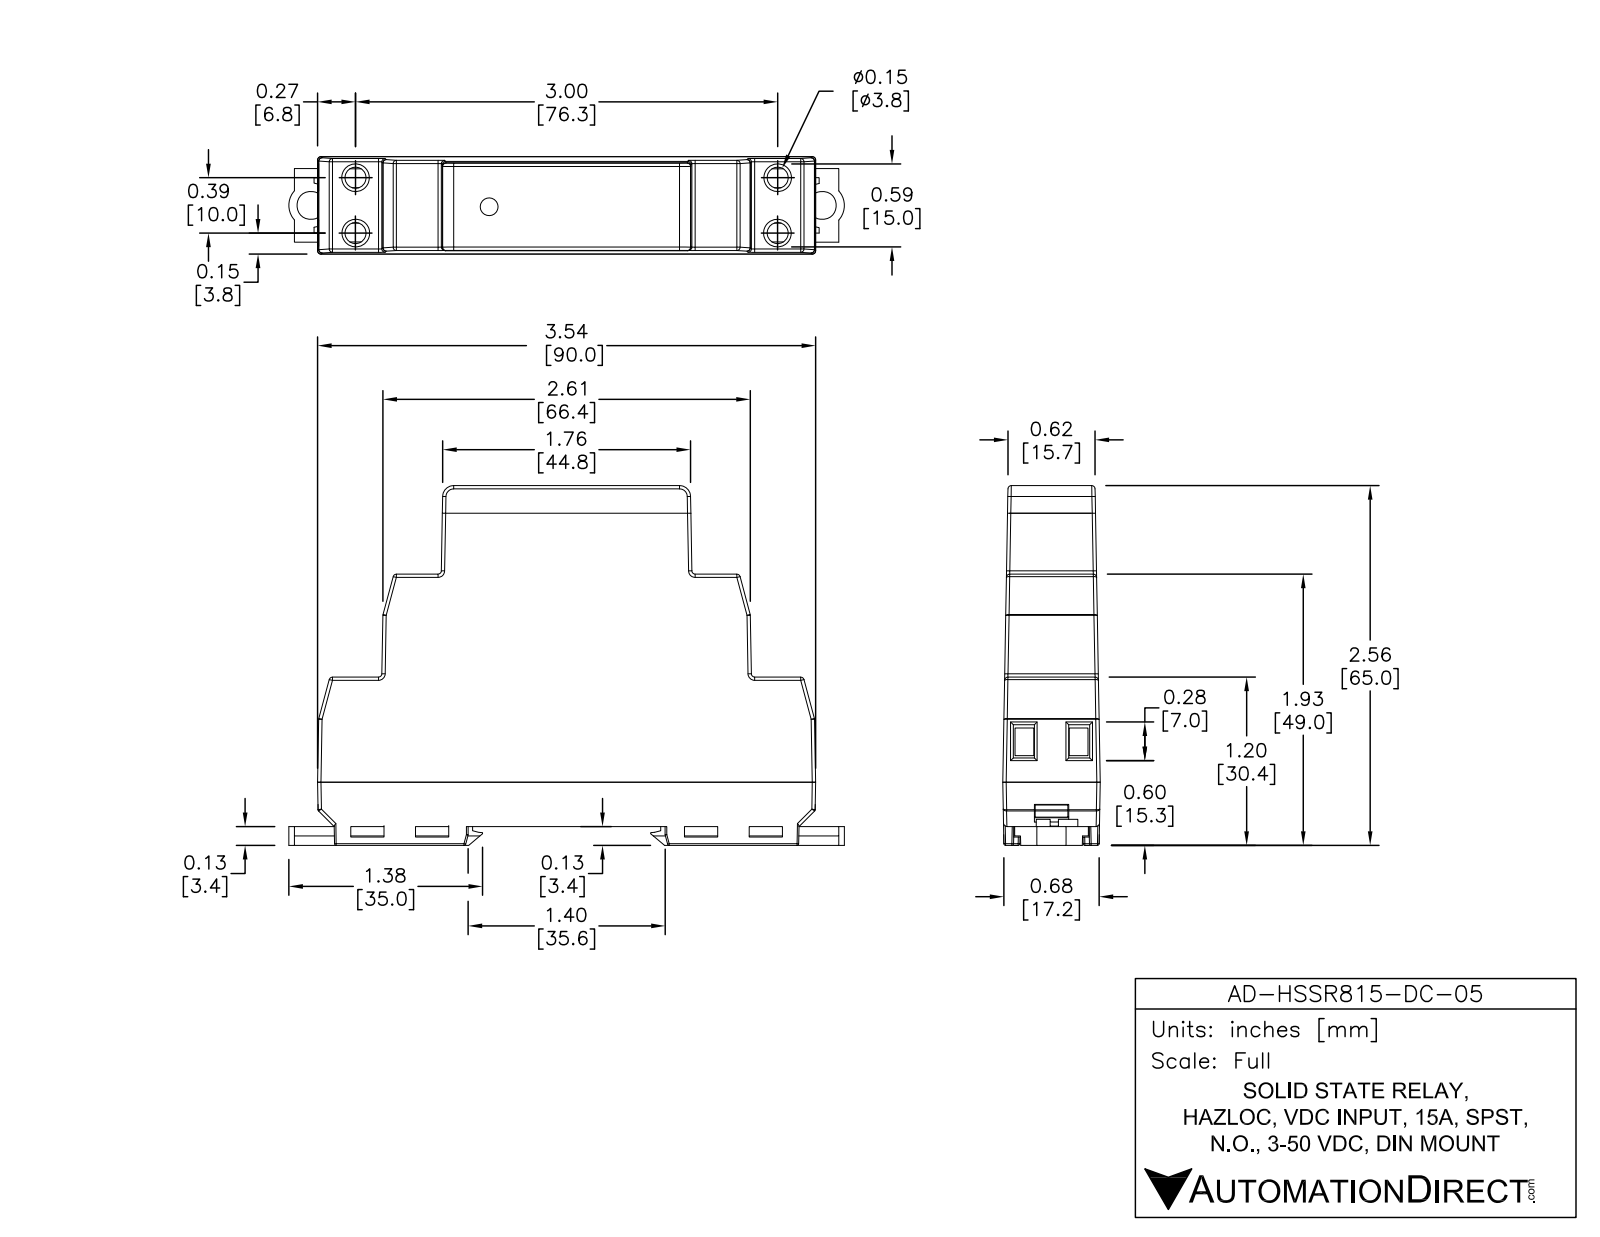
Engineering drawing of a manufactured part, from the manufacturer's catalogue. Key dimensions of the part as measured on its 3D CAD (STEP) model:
Part name (STEP PRODUCT): AD-HSSR810-DC-05
STEP written by: SolidWorks 2013 (AUTOMOTIVE_DESIGN)
Units: inches
Bodies: 35 solids, 1263 faces (684 planar, 65 cylindrical, 514 other)
Overall size (bounding box): 3.952 × 2.619 × 0.692
Volume: 4.725 in³ · Surface area: 25.56 in²
Round holes (diameter × count): ⌀0.2 ×4, ⌀0.19 ×2
Round bosses / shafts (diameter × count): ⌀0.175 ×4, ⌀0.1 ×1
Partial cylindrical surfaces — rounded edges, fillets, slot ends (radius × count): R0.02 ×10, R0.024 ×10, R0.012 ×6, R0.079 ×2, R0.15 ×2, R45.93 ×2
Main face-to-face distances: 0.136, 2.559, 2.423, 0.134, 2.425, 1.929, 1.795, 1.793, 0.63, 1.197
Hole centre spacings: 3.335, 0.379, 0.38, 0.4, 3.006, 3.033, 3.652
